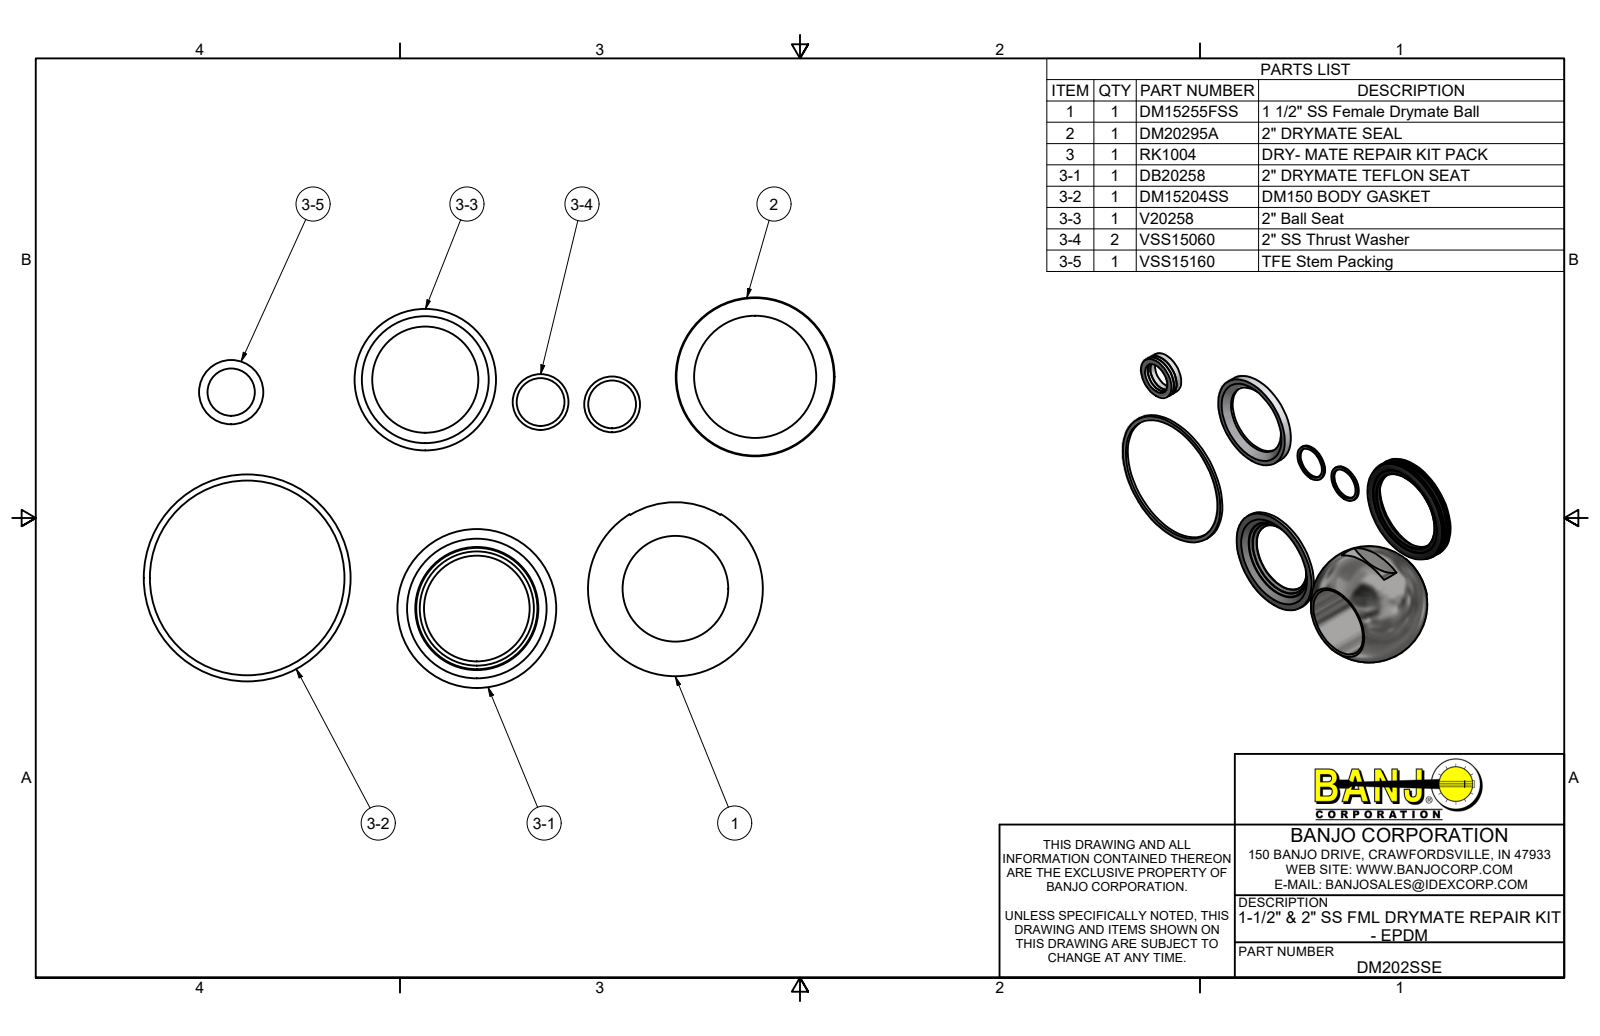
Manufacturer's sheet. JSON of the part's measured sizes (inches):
{"part_name": "DM202SSE; RK1004; DB20258; DM15204SS (+8 more)", "step_written_by": "Autodesk Inventor 2019 (AUTOMOTIVE_DESIGN)", "units": "inches", "bodies": {"solids": 10, "faces": 82, "planar": 28, "cylindrical": 23, "other": 31}, "overall_size": [9.788, 5.529, 1.91], "volume_in3": 4.695, "surface_area_in2": 50.96, "round_holes": [[1.5, 3], [0.676, 2], [0.67, 1], [1.616, 1], [1.73, 1], [2.15, 1], [2.755, 1]], "round_bosses_or_shafts": [[2.25, 2], [0.79, 2], [2.932, 1], [2, 1], [0.913, 1]], "partial_cylinders_radius": [[1.18, 1]], "face_to_face_distances": [0.17, 0.235, 0.065, 0.11, 0.06, 0.175, 0.03, 0.015, 0.052, 0.183], "hole_center_spacings": [1.014, 1.664, 2.063, 2.639, 2.67, 2.755, 2.759, 2.826]}
